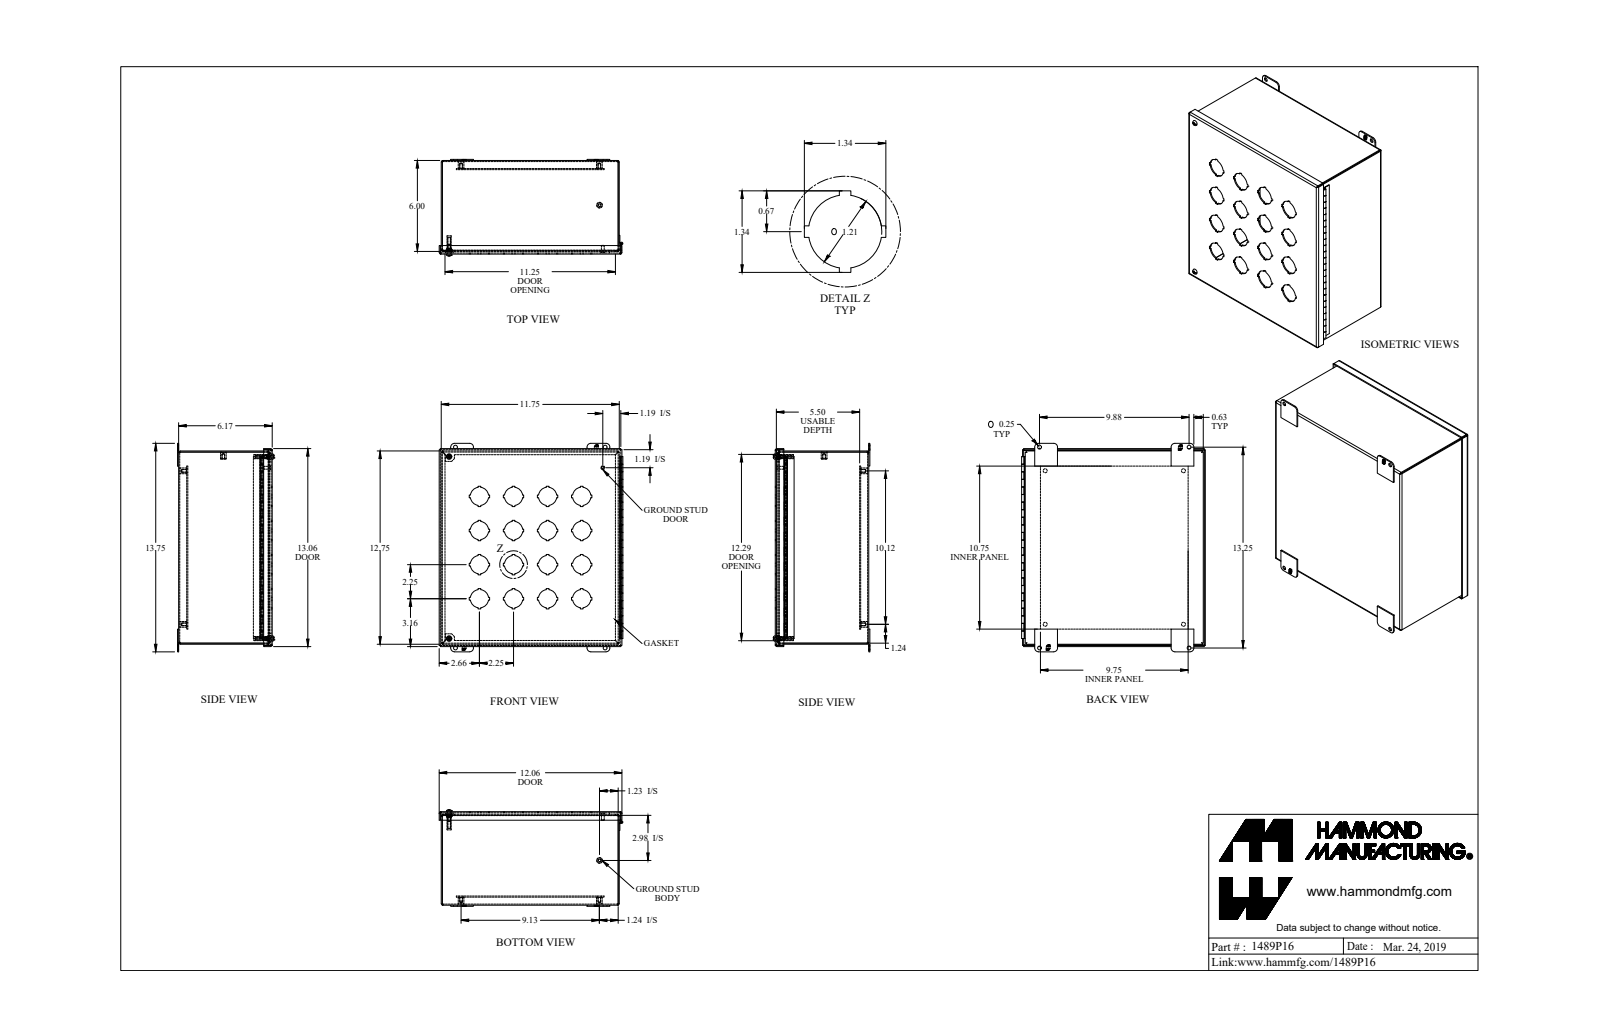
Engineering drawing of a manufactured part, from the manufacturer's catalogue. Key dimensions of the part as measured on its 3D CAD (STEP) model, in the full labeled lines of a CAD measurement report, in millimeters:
Part name (STEP PRODUCT): 1489P16_Default
STEP written by: SolidWorks 2019 (CONFIG_CONTROL_DESIGN)
Units: millimetres
Bodies: 21 solids, 985 faces (681 planar, 246 cylindrical, 58 other)
Overall size (bounding box): 349.3 × 307.9 × 161.8
Volume: 970 400 mm³ · Surface area: 1 024 000 mm²
Round holes (diameter × count): ⌀30.7 ×16, ⌀6.4 ×6, ⌀4 ×5, ⌀6.7 ×4, ⌀4 ×2, ⌀10.3 ×2
Round bosses / shafts (diameter × count): ⌀9.5 ×5, ⌀9.9 ×2, ⌀7 ×2, ⌀4.8 ×2, ⌀3.8 ×2, ⌀6.4 ×1, ⌀4.8 ×1, ⌀4.4 ×1
Partial cylindrical surfaces — rounded edges, fillets, slot ends (radius × count): R0.9 ×12, R2.7 ×12, R6.4 ×8, R4.1 ×2, R4.3 ×2
Main face-to-face distances: 1.8, 154.9, 141.4, 13.5, 296.6, 1.8, 153.1, 156.8, 322, 15.3
Hole centre spacings: 57.2, 127.8, 80.8, 114.3, 180.7, 161.6, 171.5, 206.1
